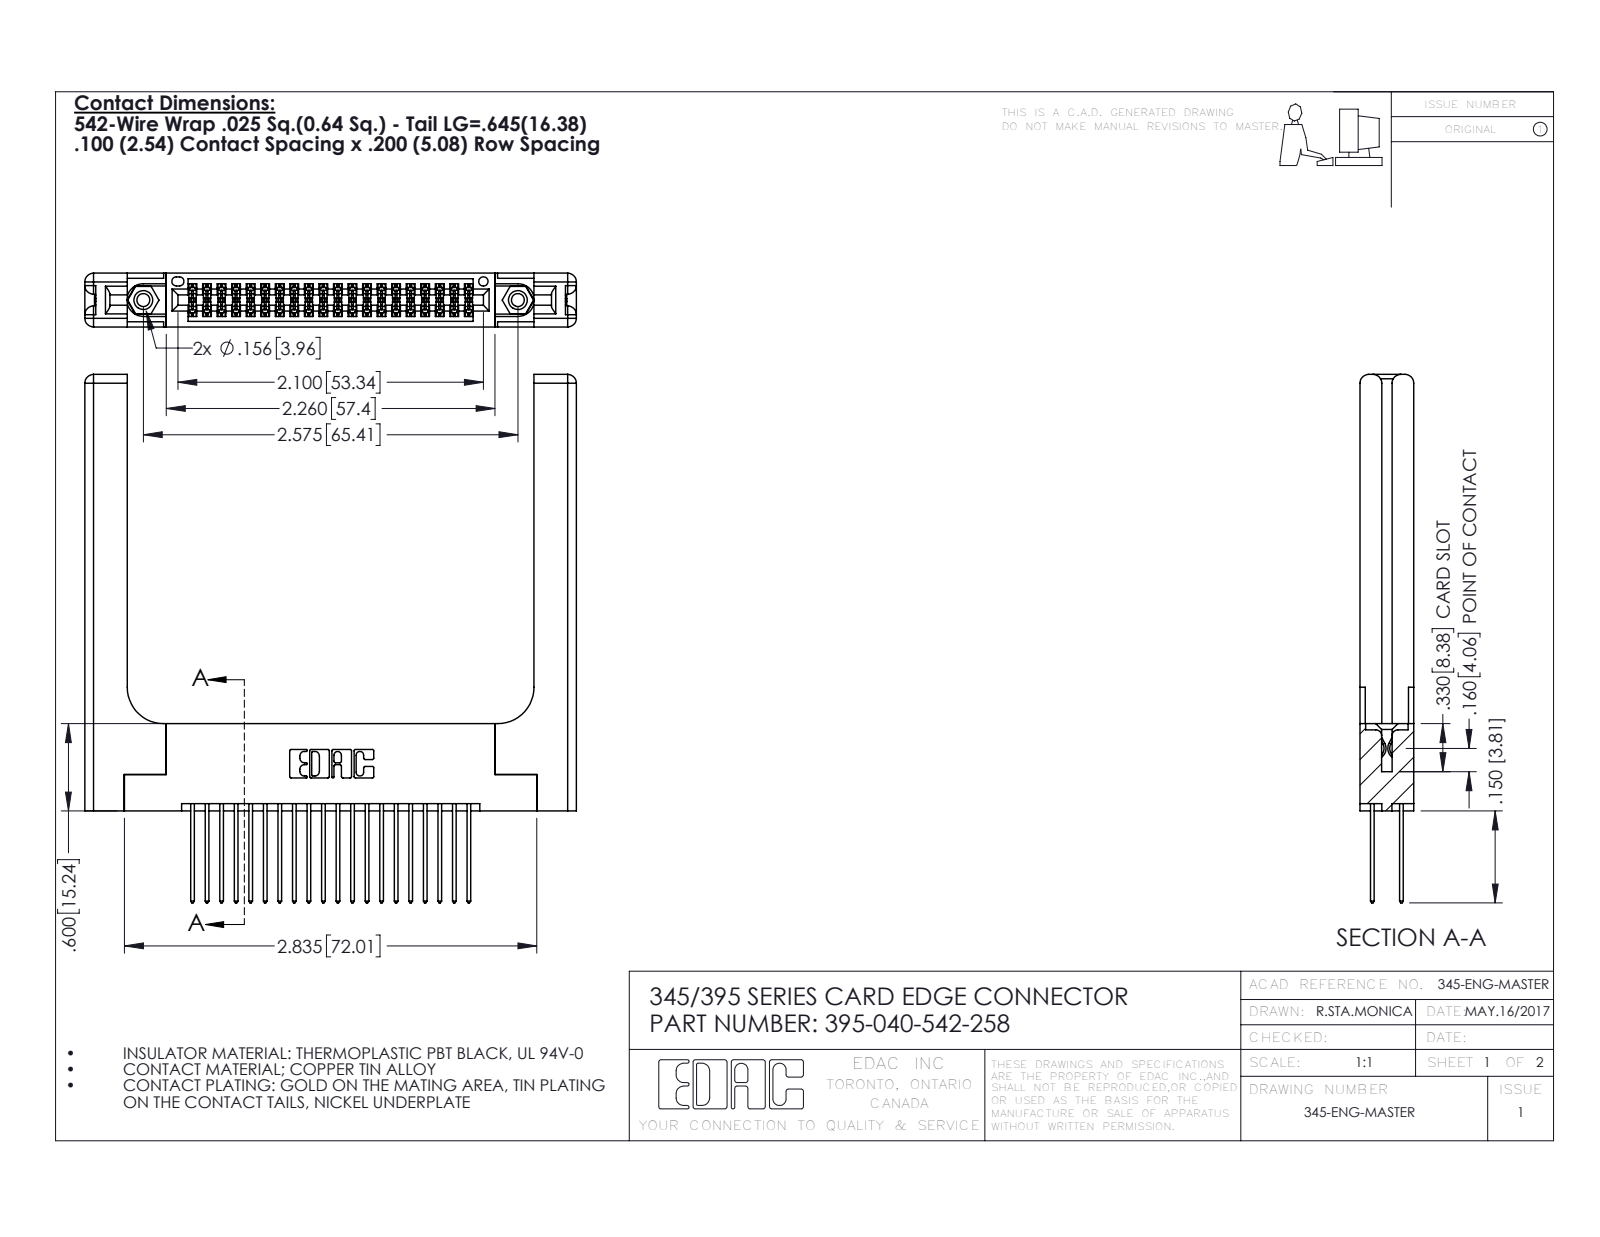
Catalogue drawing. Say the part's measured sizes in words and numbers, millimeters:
The part is named "345-220-058_345-220-058; 345 Part_Flush Mounting Lugs - 0.156 Dia-TH; 395-040-542-258; 345-292-001_345-293-142 (+1 more)". Its 3-D file was written by "SolidWorks 2016 (CONFIG_CONTROL_DESIGN)". It is 45 solids with 2382 faces: 1548 planar, 774 cylindrical and 60 other. Overall it measures 92.3 by 85.8 by 9.4 millimeters. Its volume is 16 800 cubic millimeters and its surface area 17 800 square millimeters. Round holes: 2 of diameter 2.3, 2 of diameter 3.2, 2 of diameter 4, 1 of diameter 1.6. Round bosses or shafts: 2 of diameter 3.9. Partial cylindrical surfaces (rounded edges, fillets, slot ends): 60 of radius 0.2, 40 of radius 0.3, 22 of radius 0.3, 16 of radius 1.5, 6 of radius 0.2, 6 of radius 0.8, 3 of radius 0.7, 2 of radius 0.4. The main face-to-face distances are 9.4, 1.8, 7.6, 5.1, 2.5, 6.9, 0.6, 5.7, 3.8, 3.8. The hole center spacings are 6.9, 59.5, 65.4.
